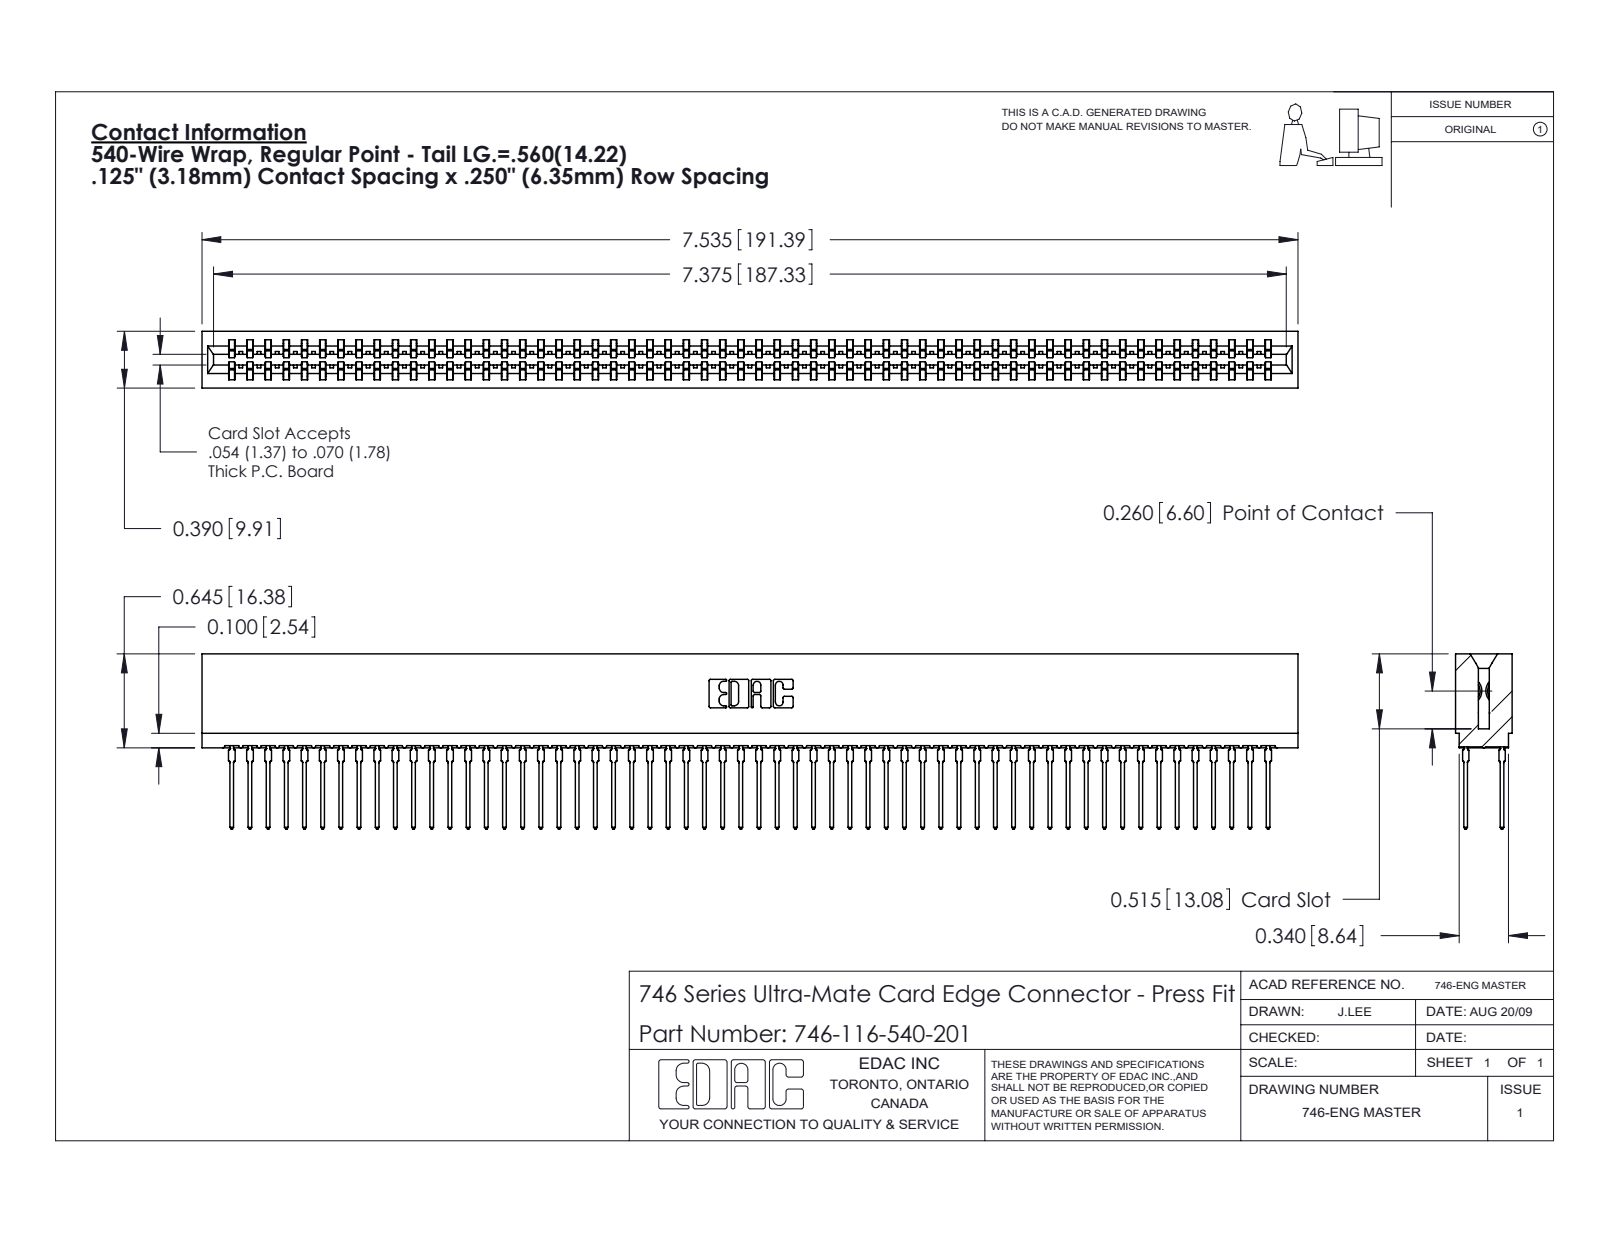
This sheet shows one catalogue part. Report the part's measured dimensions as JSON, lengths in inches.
{"part_name": "746-116-540-201; 746-292-001_540; 746 Part_.515 Slot Depth - 01", "step_written_by": "SolidWorks 2020 (CONFIG_CONTROL_DESIGN)", "units": "inches", "bodies": {"solids": 117, "faces": 10479, "planar": 5391, "cylindrical": 2072, "other": 3016}, "overall_size": [7.535, 1.204, 0.39], "volume_in3": 1.267, "surface_area_in2": 54.7, "partial_cylinders_radius": [[0.021, 232], [0.015, 59], [0.01, 22], [0.005, 8], [0.011, 8], [0.007, 6], [0.031, 6], [0.026, 3]], "face_to_face_distances": [0.057, 0.333, 0.25, 0.39, 0.025, 0.307, 0.275, 0.083, 0.174, 0.158]}
